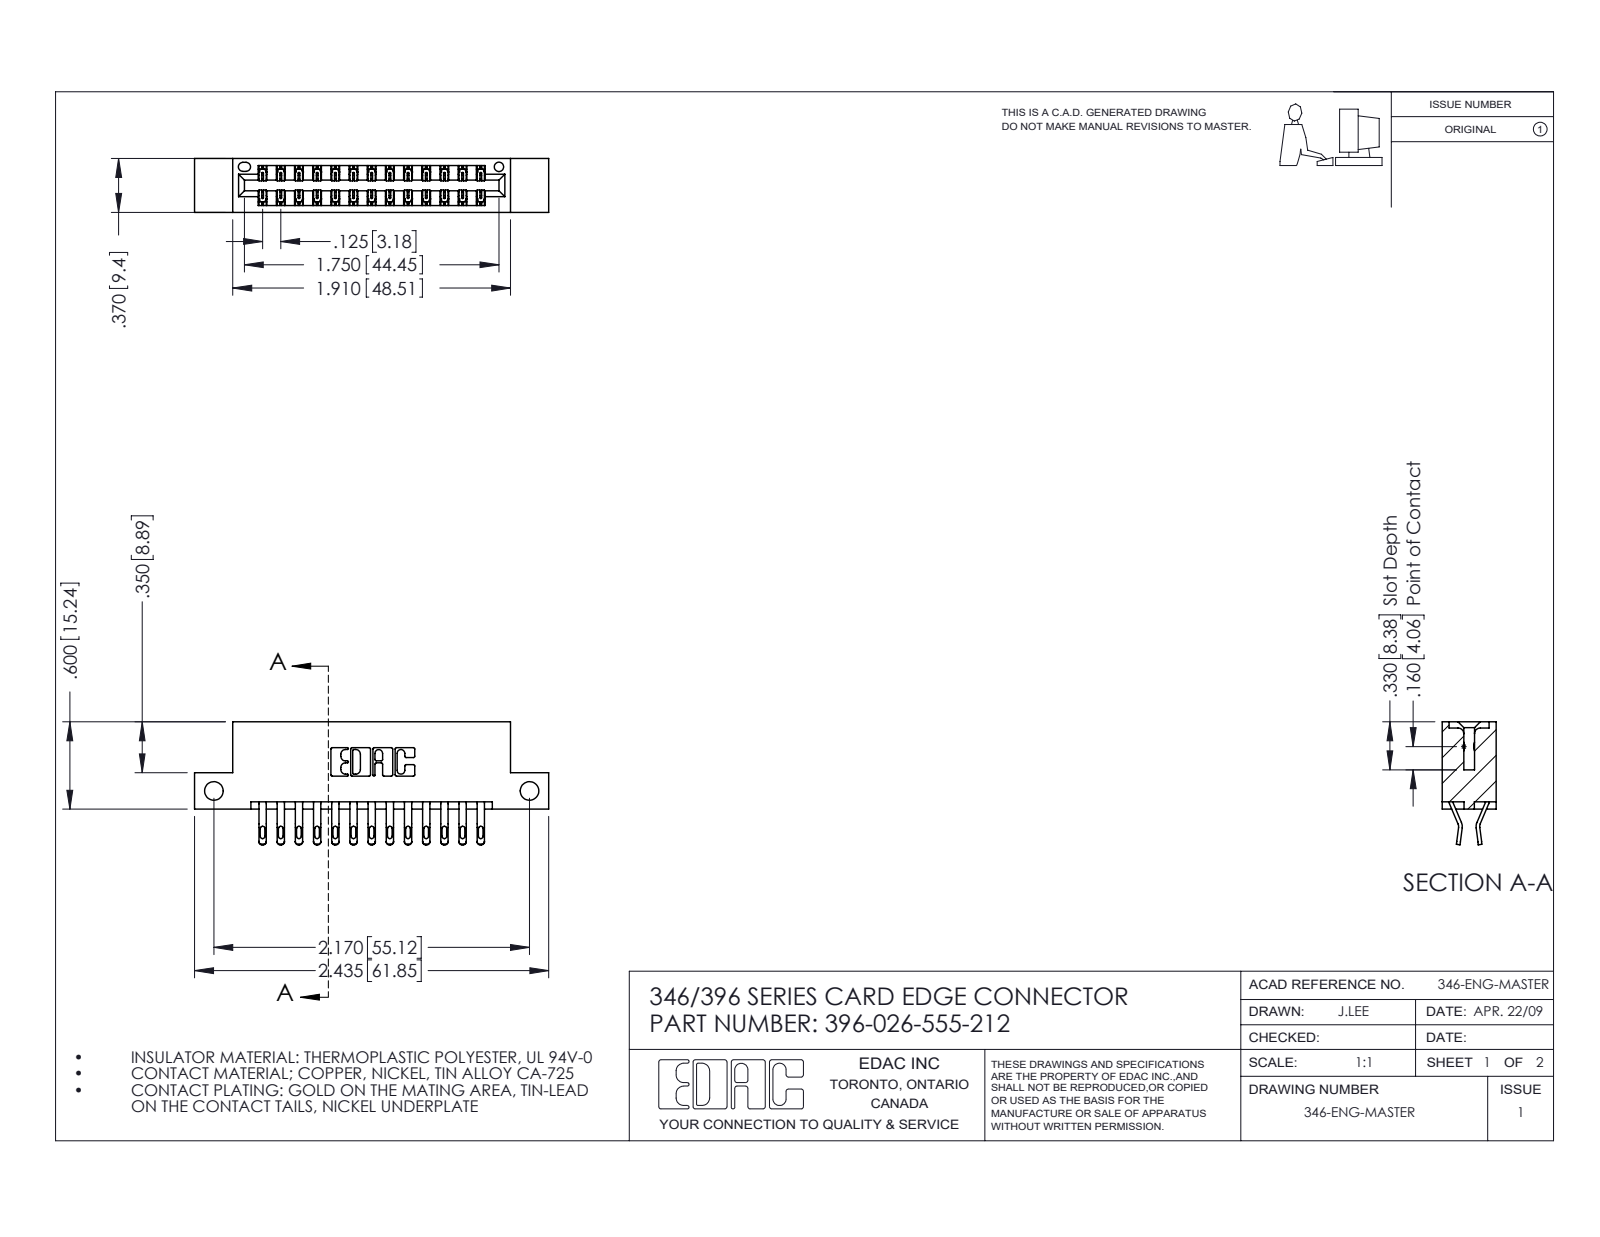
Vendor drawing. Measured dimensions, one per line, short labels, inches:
name: 345-292-001_555 Tail; 346 Part_Flush Mounting Lugs - Side Mount; 396-026-555-212
written by: SolidWorks 2016 (CONFIG_CONTROL_DESIGN)
unit: in
bodies: 27 solids, 1630 faces (934 planar, 696 cylindrical, 0 other)
size: 2.435 × 0.845 × 0.37
volume: 0.354 in³; area: 11.84 in²
holes: 2× ⌀0.128, 1× ⌀0.064
rounds: 52× R0.016, 52× R0.02, 39× R0.006, 22× R0.01, 6× R0.007, 6× R0.031, 3× R0.026, 2× R0.01
face distances: 0.25, 0.048, 0.322, 0.37, 0.025, 0.072, 0.298, 0.275, 0.148, 0.222
hole spacings: 2.17
